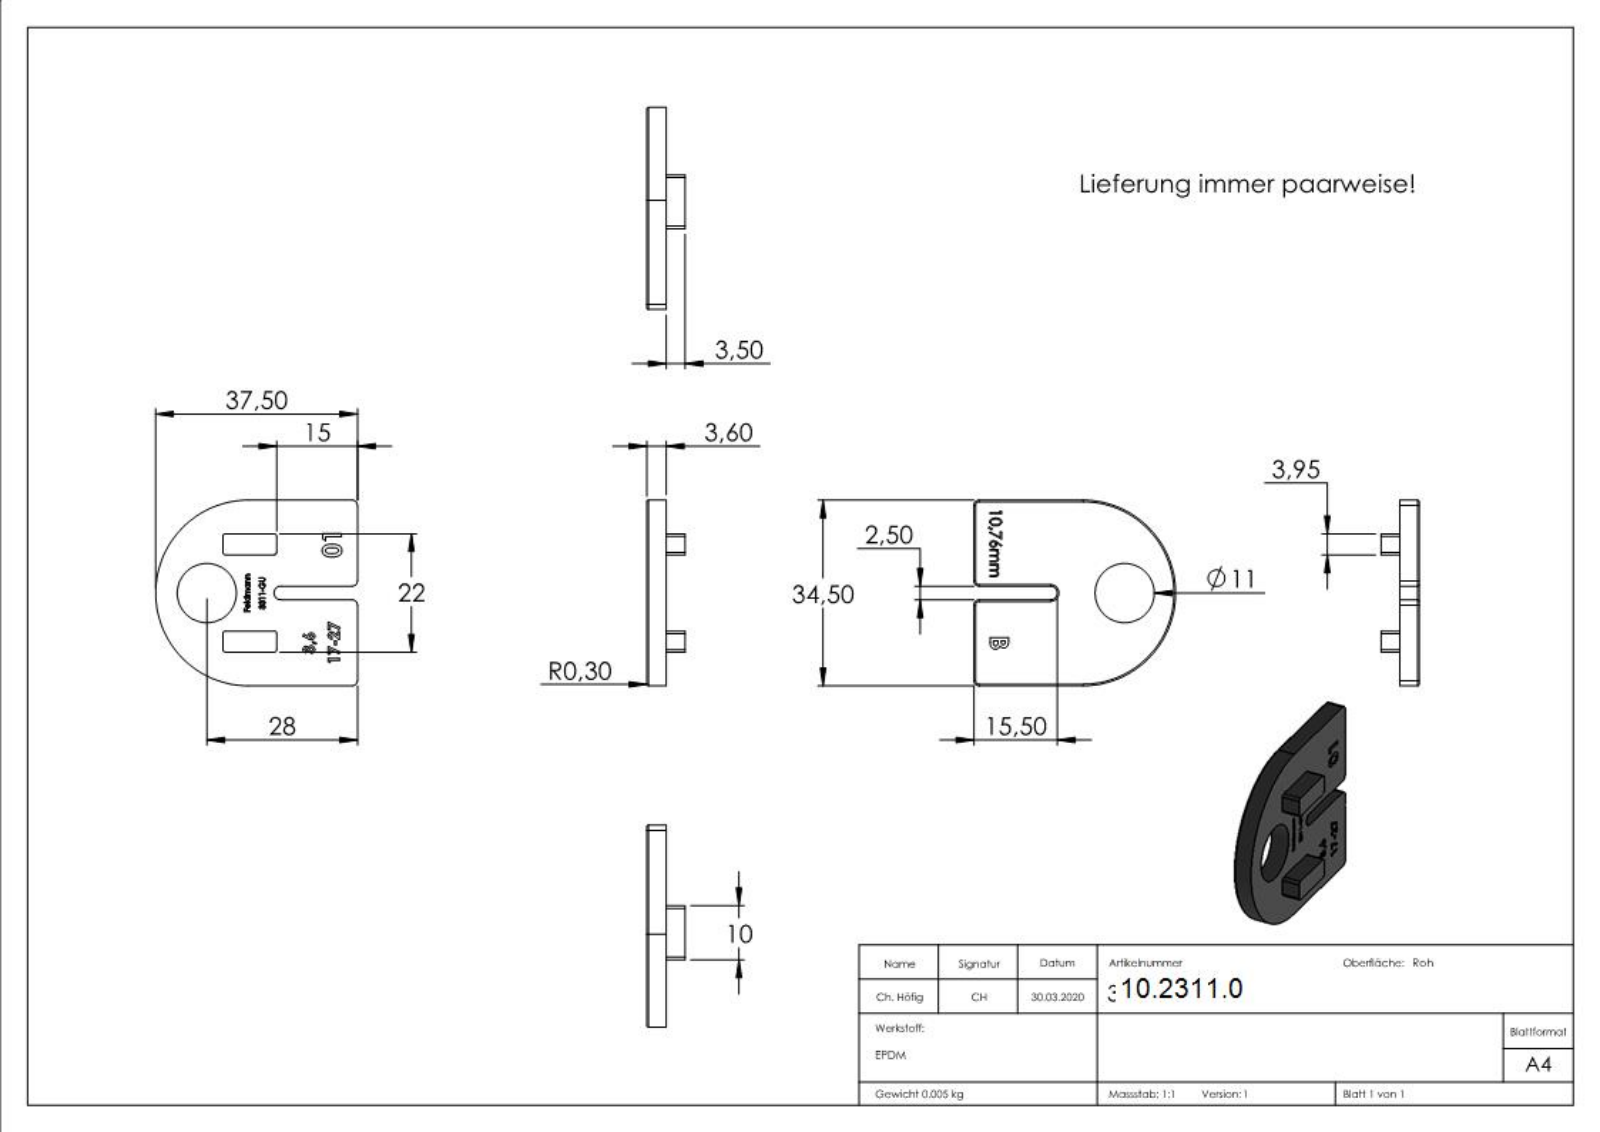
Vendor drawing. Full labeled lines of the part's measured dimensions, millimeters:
Part name (STEP PRODUCT): 3311-GU
STEP written by: SolidWorks 2015 (CONFIG_CONTROL_DESIGN)
Units: millimetres
Bodies: 1 solid, 444 faces (243 planar, 21 cylindrical, 180 other)
Overall size (bounding box): 37.5 × 34.5 × 7.1
Volume: 3 984 mm³ · Surface area: 2 946 mm²
Round holes (diameter × count): ⌀11 ×1
Partial cylindrical surfaces — rounded edges, fillets, slot ends (radius × count): R0.5 ×8, R0.3 ×5, R1 ×4, R1.25 ×1, R17.25 ×1
Main face-to-face distances: 3.6, 3.5, 18.5, 16, 7.1, 34.5, 6.25, 10.2, 24.3, 28.25
